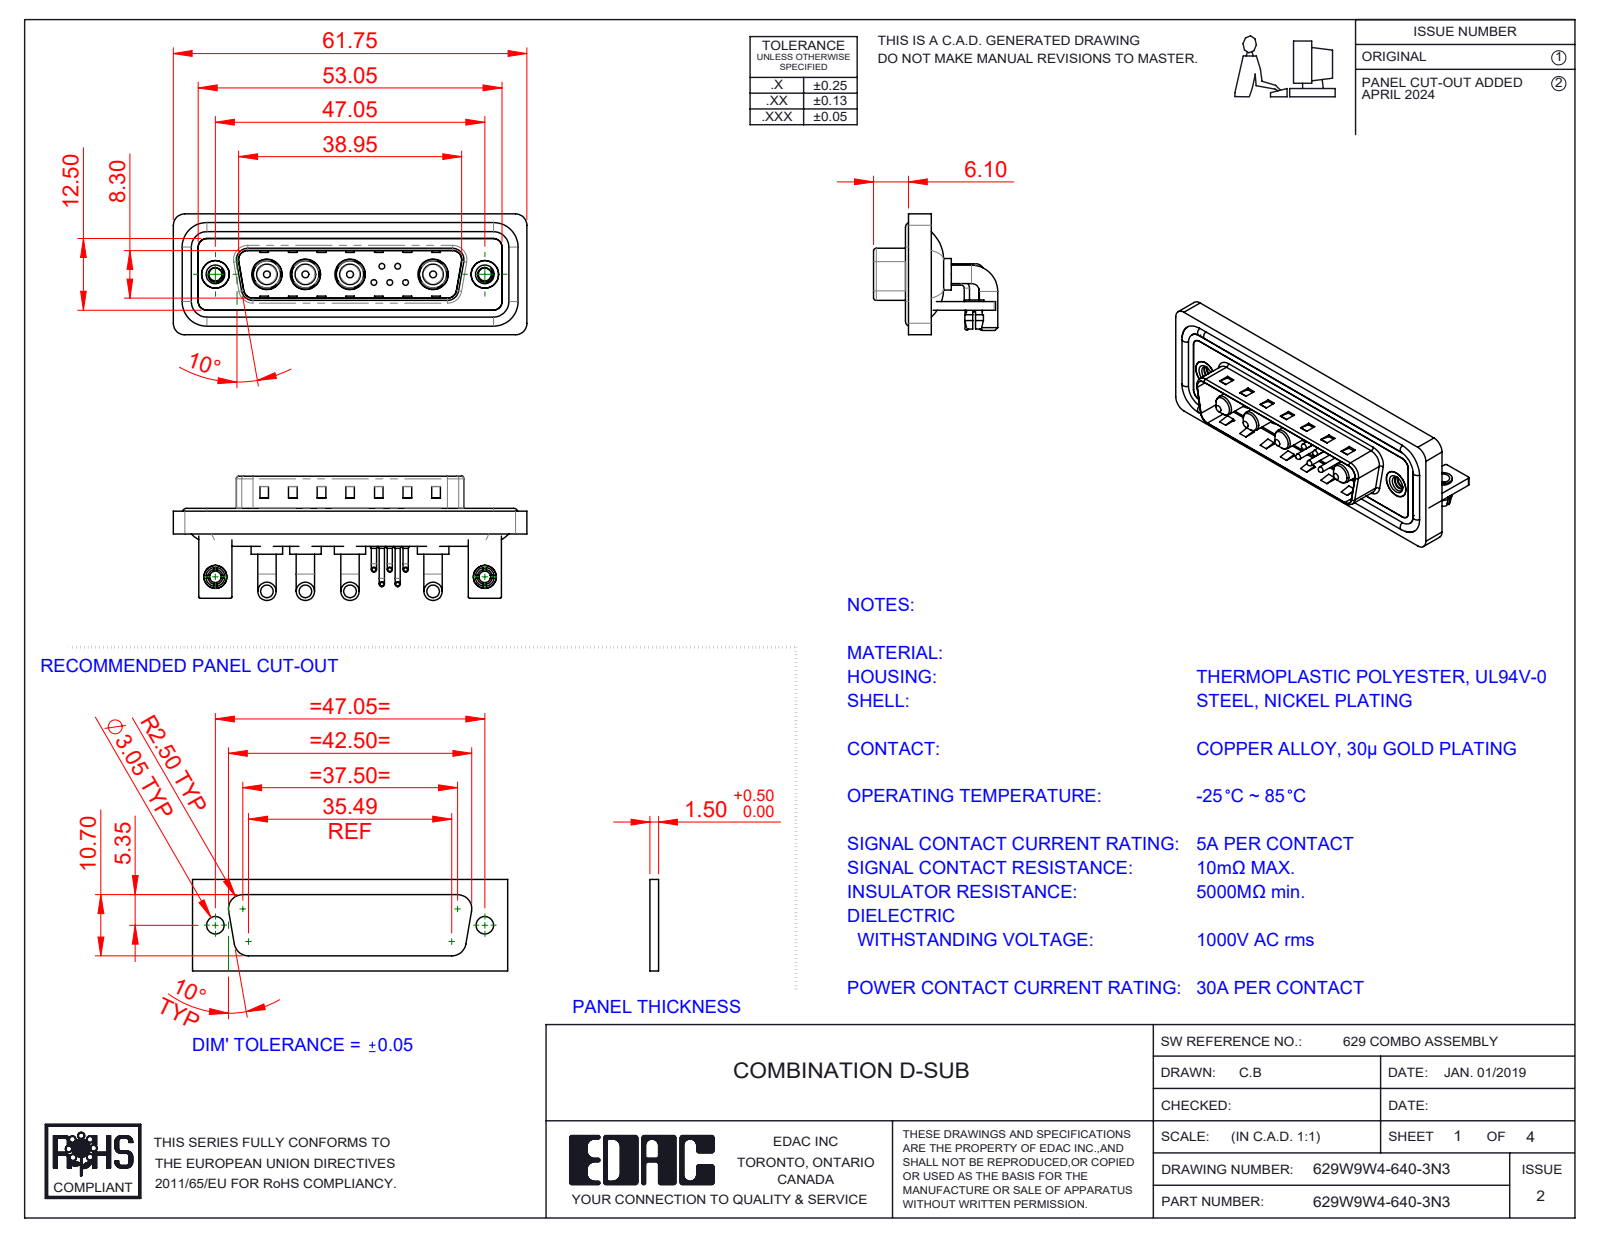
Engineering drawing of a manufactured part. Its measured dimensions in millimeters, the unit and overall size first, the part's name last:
Units: millimetres
Overall size (bounding box): 61.75 × 21.7 × 21.1
Round holes (diameter × count): ⌀2 ×7, ⌀0.75 ×5, ⌀1.6 ×5, ⌀4.85 ×4, ⌀5.3 ×4, ⌀2.26 ×2, ⌀2.5 ×2, ⌀3.2 ×2, ⌀4 ×2, ⌀4.8 ×2, ⌀5 ×2
Round bosses / shafts (diameter × count): ⌀0.9 ×10, ⌀3.2 ×8, ⌀1.5 ×5, ⌀1 ×5, ⌀0.65 ×5, ⌀5.5 ×4, ⌀5.2 ×4, ⌀4.75 ×4
Partial cylindrical surfaces — rounded edges, fillets, slot ends (radius × count): R2 ×19, R1.5 ×18, R0.25 ×16, R0.5 ×9, R1.6 ×8, R1.01 ×5, R0.6 ×4, R0.65 ×4
Main face-to-face distances: 0.4, 1.5, 0.8, 2.9, 2.1, 1.1, 3.7, 4.1, 4.5, 1.6
Hole centre spacings: 3.16, 2.77, 5.04, 14.5, 47.05, 2.78, 4.4, 4.41
Volume: 8 130 mm³ · Surface area: 13 248 mm²
Bodies: 24 solids, 1337 faces (637 planar, 502 cylindrical, 198 other)
Part name (STEP PRODUCT): 629Combo Contact Row 1; 629Combo Stabilizer Bracket; 629Combo Housing_9W4; 629Combo Shell Front_25 Contacts (+7 more)
STEP written by: SolidWorks 2023 (CONFIG_CONTROL_DESIGN)
